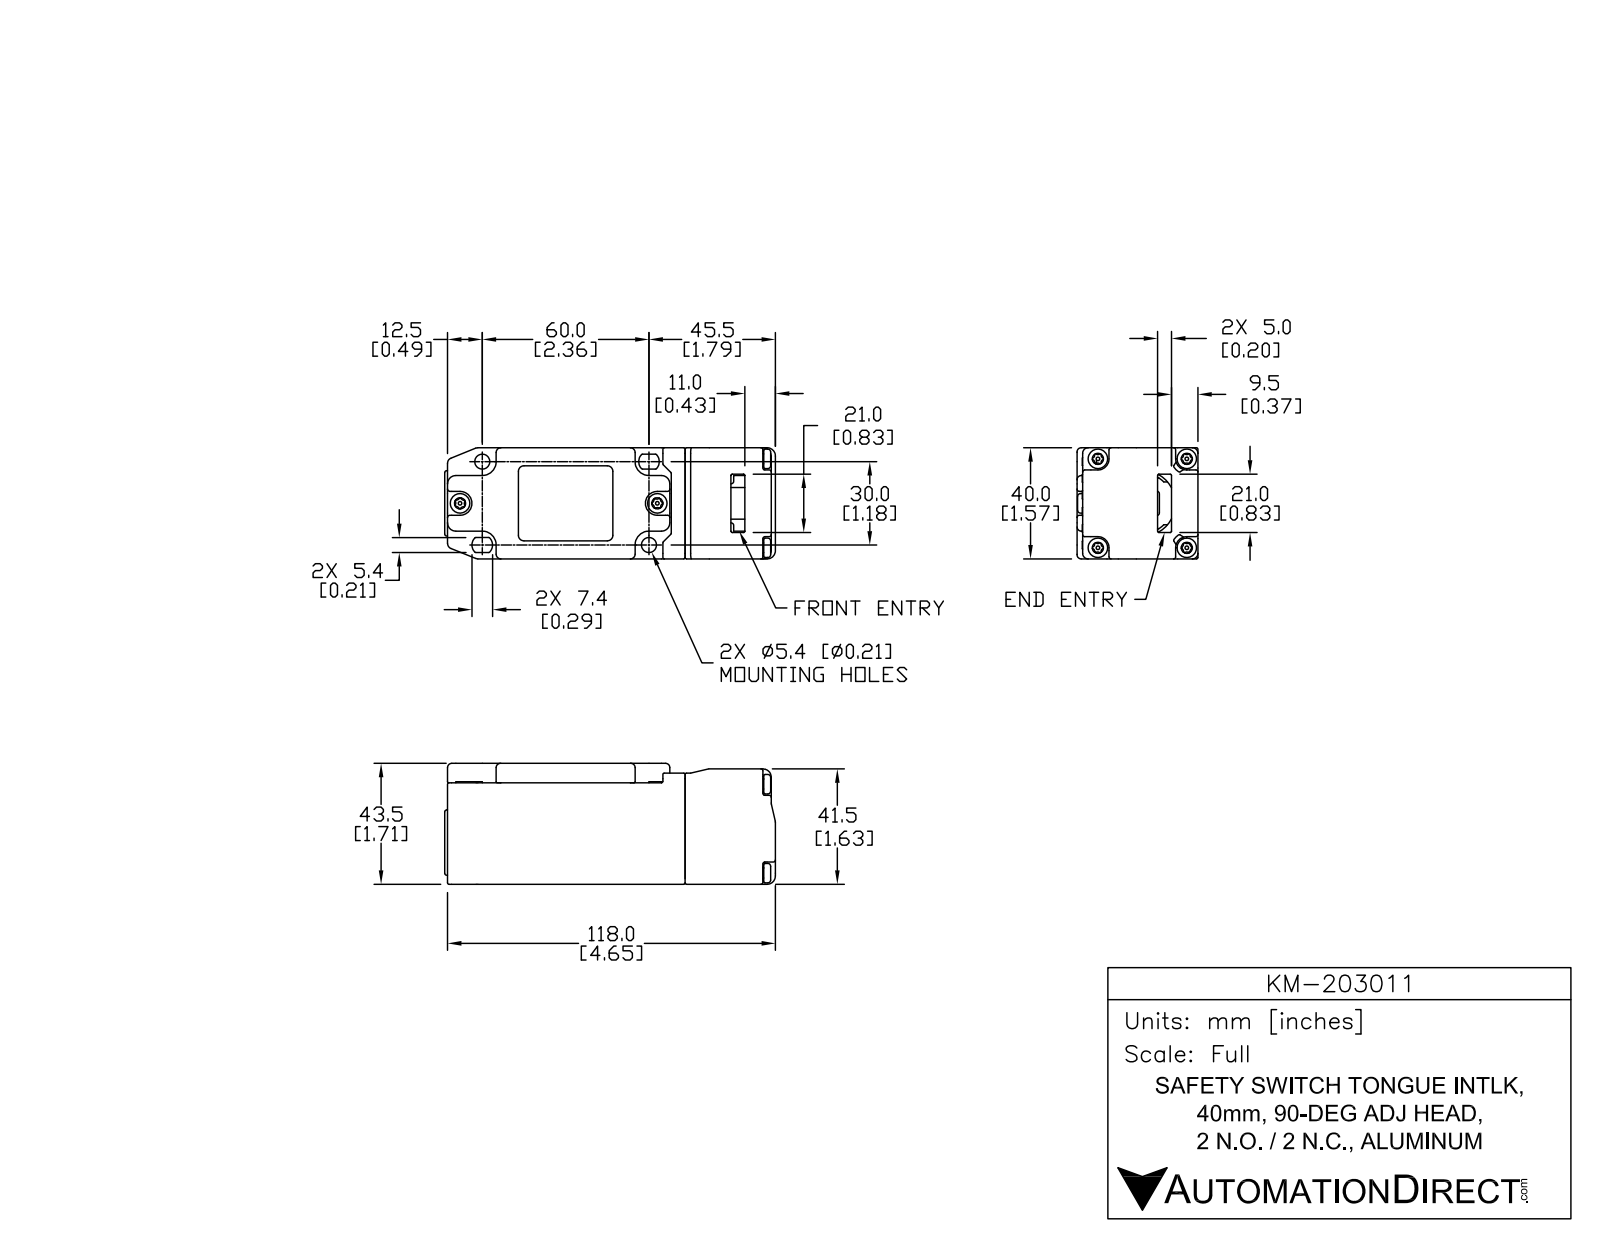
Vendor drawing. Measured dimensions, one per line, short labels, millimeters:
name: KM-2030011
written by: SolidWorks 2013 (AUTOMOTIVE_DESIGN)
unit: mm
bodies: 1 solid, 581 faces (128 planar, 263 cylindrical, 190 other)
size: 119.63 × 43.56 × 40
volume: 183 300 mm³; area: 28 465 mm²
holes: 2× ⌀5.4
bosses: 4× ⌀6.77, 2× ⌀6.63, 1× ⌀23, 1× ⌀5.6
rounds: 95× R0.5, 68× R0.25, 5× R3, 4× R1.45, 4× R1.7, 4× R2.75, 4× R4, 4× R5
face distances: 40, 43.5, 0.5, 43, 118, 2.6, 5, 9.5, 102, 16
hole spacings: 67.08
